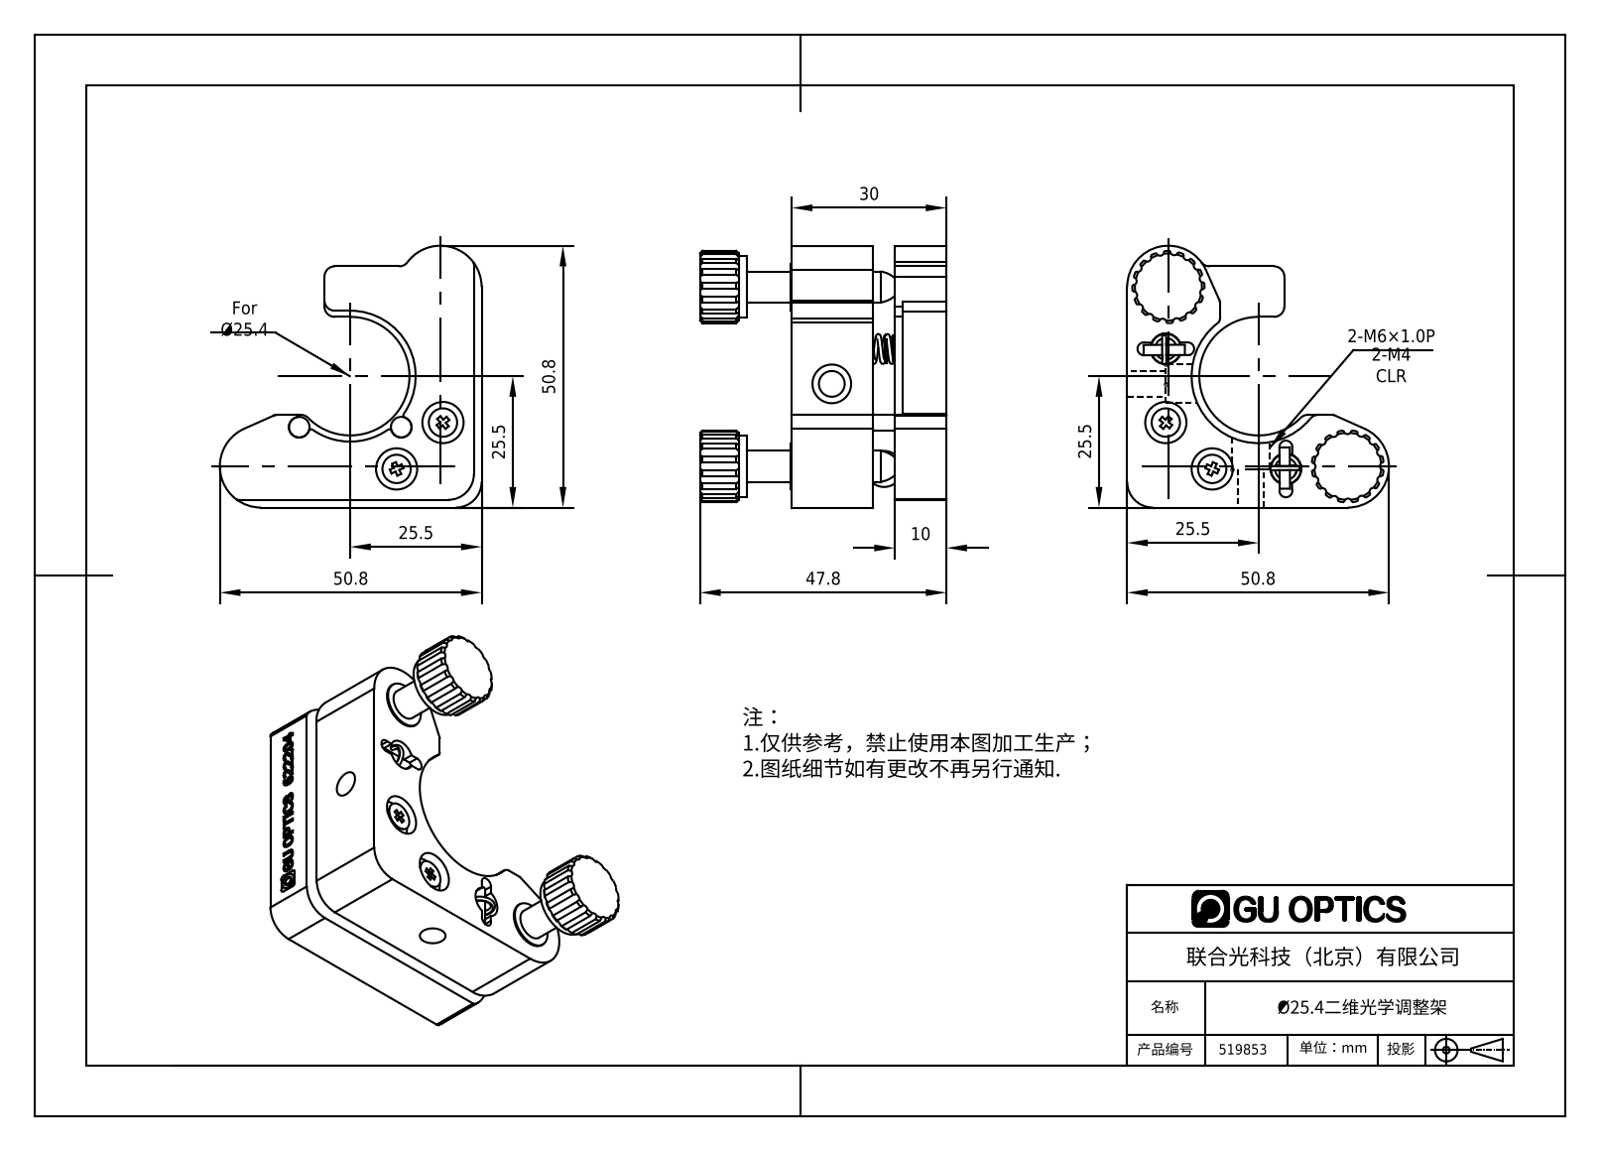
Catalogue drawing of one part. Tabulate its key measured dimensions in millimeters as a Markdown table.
| quantity | value |
| --- | --- |
| part name | 519853 |
| STEP written by | SolidWorks 2016 (AUTOMOTIVE_DESIGN) |
| units | millimeters |
| bodies | 0 solids, 632 faces (210 planar, 205 cylindrical, 217 other) |
| overall size | 50.8 × 50.8 × 47.8 |
| round holes (diameter × count) | 6 × 4, 8 × 4, 4 × 3, 5 × 2, 7.5 × 2, 3.5 × 1 |
| round bosses / shafts (diameter × count) | 12 × 2, 9 × 2, 5.4 × 2, 3 × 2, 2 × 2, 0.8 × 2, 4 × 1 |
| partial cylindrical surfaces (radius × count) | 0.75 × 32, 2 × 7, 1 × 6, 1.25 × 4, 0.5 × 3, 5 × 2, 7 × 2, 8 × 2 |
| main face-to-face distances | 10, 4.2, 14.2, 15.8, 20, 30, 1.5, 37.8, 30.3, 17.8 |
| hole center spacings | 8.15, 12.01, 14.3, 17.22, 24.98, 26.3, 28.24, 36.31 |
